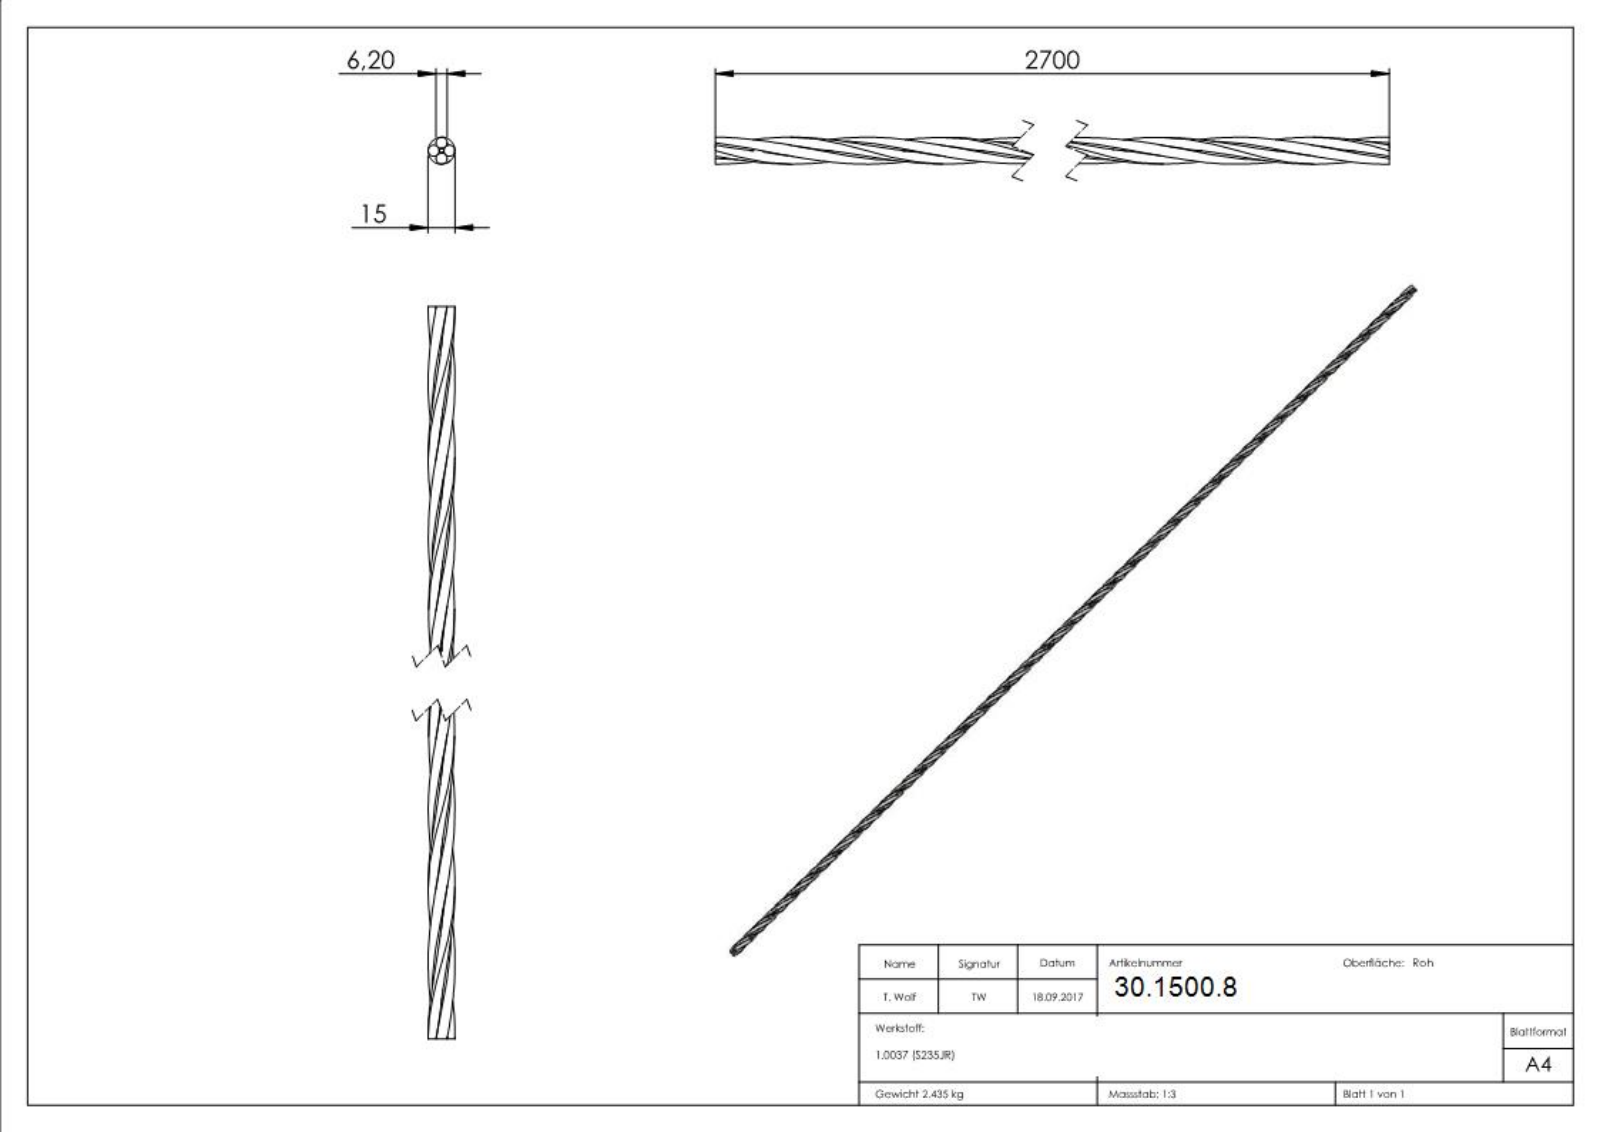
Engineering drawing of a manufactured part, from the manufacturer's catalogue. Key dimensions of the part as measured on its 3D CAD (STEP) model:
Part name (STEP PRODUCT): 2015
STEP written by: SolidWorks 2015 (CONFIG_CONTROL_DESIGN)
Units: millimetres
Bodies: 4 solids, 129 faces (73 planar, 0 cylindrical, 56 other)
Overall size (bounding box): 2700 × 15.05 × 15.02
Volume: 337 567 mm³ · Surface area: 208 085 mm²
Main face-to-face distances: 2700, 1.78, 0.5, 2699.5, 0.44, 0.67, 0.83, 0.99, 1.21, 2.45
